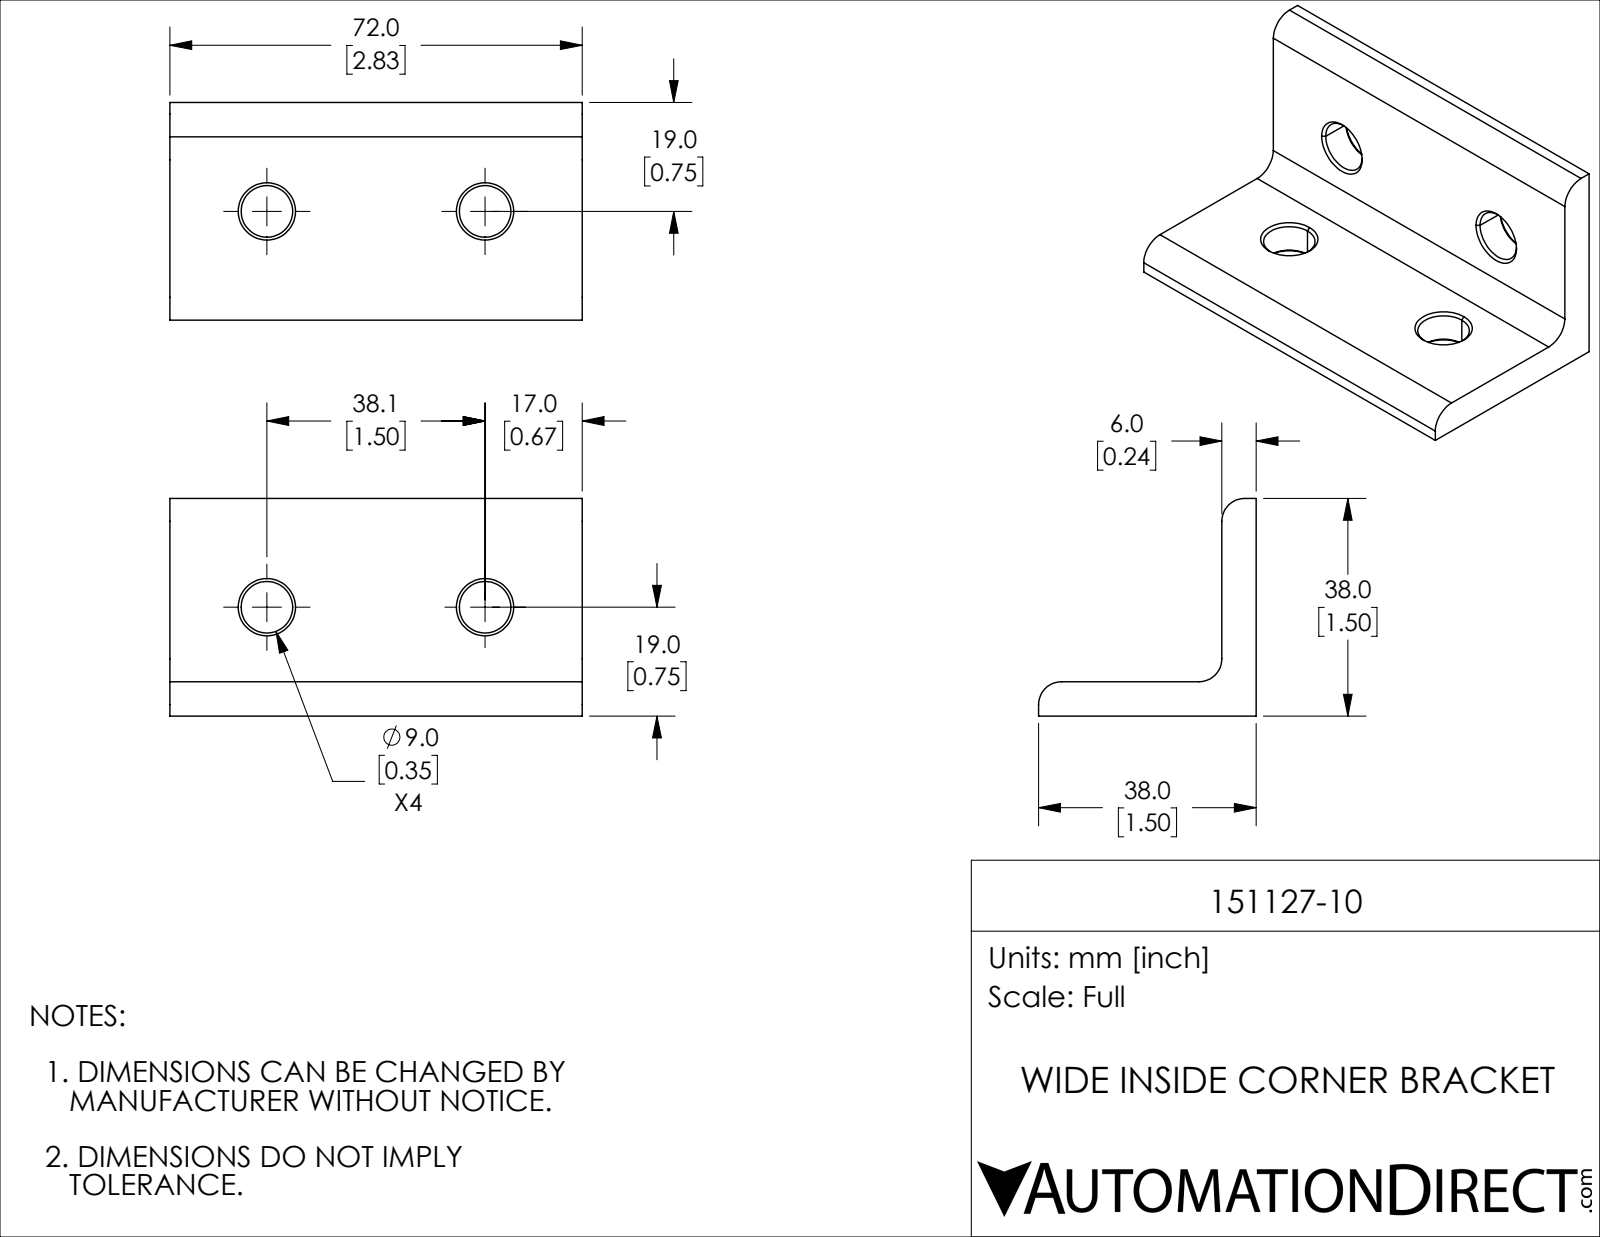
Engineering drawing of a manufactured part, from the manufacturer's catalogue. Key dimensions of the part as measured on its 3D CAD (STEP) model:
Part name (STEP PRODUCT): 151127-10
STEP written by: SolidWorks 2024 (CONFIG_CONTROL_DESIGN)
Units: millimetres
Bodies: 1 solid, 35 faces (8 planar, 11 cylindrical, 16 other)
Overall size (bounding box): 72 × 38 × 38
Volume: 28 437 mm³ · Surface area: 11 512 mm²
Round holes (diameter × count): ⌀9 ×4
Partial cylindrical surfaces — rounded edges, fillets, slot ends (radius × count): R4 ×3
Main face-to-face distances: 6, 72, 38, 32
Hole centre spacings: 38.1
